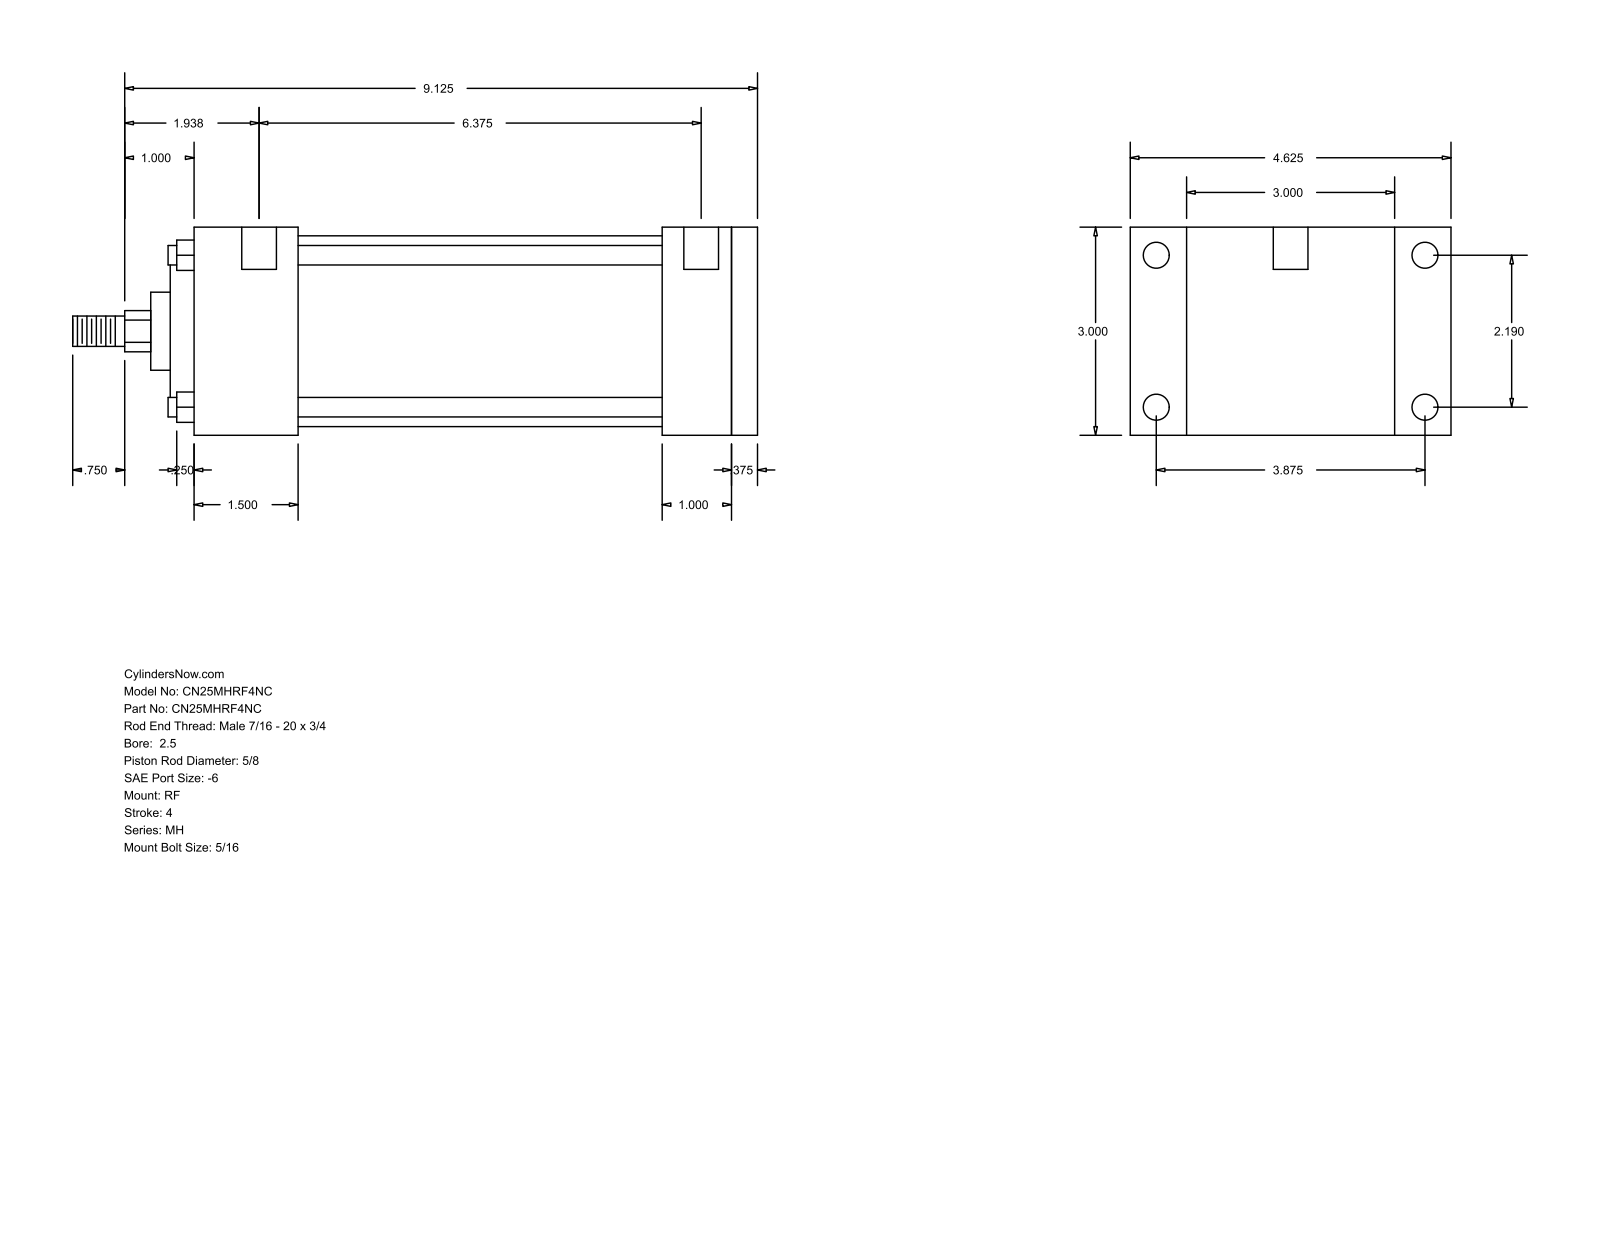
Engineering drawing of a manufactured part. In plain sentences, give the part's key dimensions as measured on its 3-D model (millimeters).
The part is named "MH_RF__0250_0.625". Its 3-D file was written by "GSSL Pune (CONFIG_CONTROL_DESIGN)". It is 0 solids with 94 faces: 65 planar, 29 cylindrical and 0 other. Overall it measures 250.82 by 117.47 by 76.2 millimeters. Round holes: 4 of diameter 5.56, 4 of diameter 9.53, 2 of diameter 12.7. Round bosses or shafts: 4 of diameter 7.14, 1 of diameter 69.85, 1 of diameter 55.55, 1 of diameter 28.57, 1 of diameter 15.88, 1 of diameter 11.11. Partial cylindrical surfaces (rounded edges, fillets, slot ends): 1 of radius 7.54. The main face-to-face distances are 76.2, 9.53, 206.38, 196.85, 25.4, 34.93, 38.1, 171.45, 133.35, 158.75. The hole center spacings are 55.62, 98.42, 113.05, 169.86, 3.17, 4.76, 161.93, 165.1.
